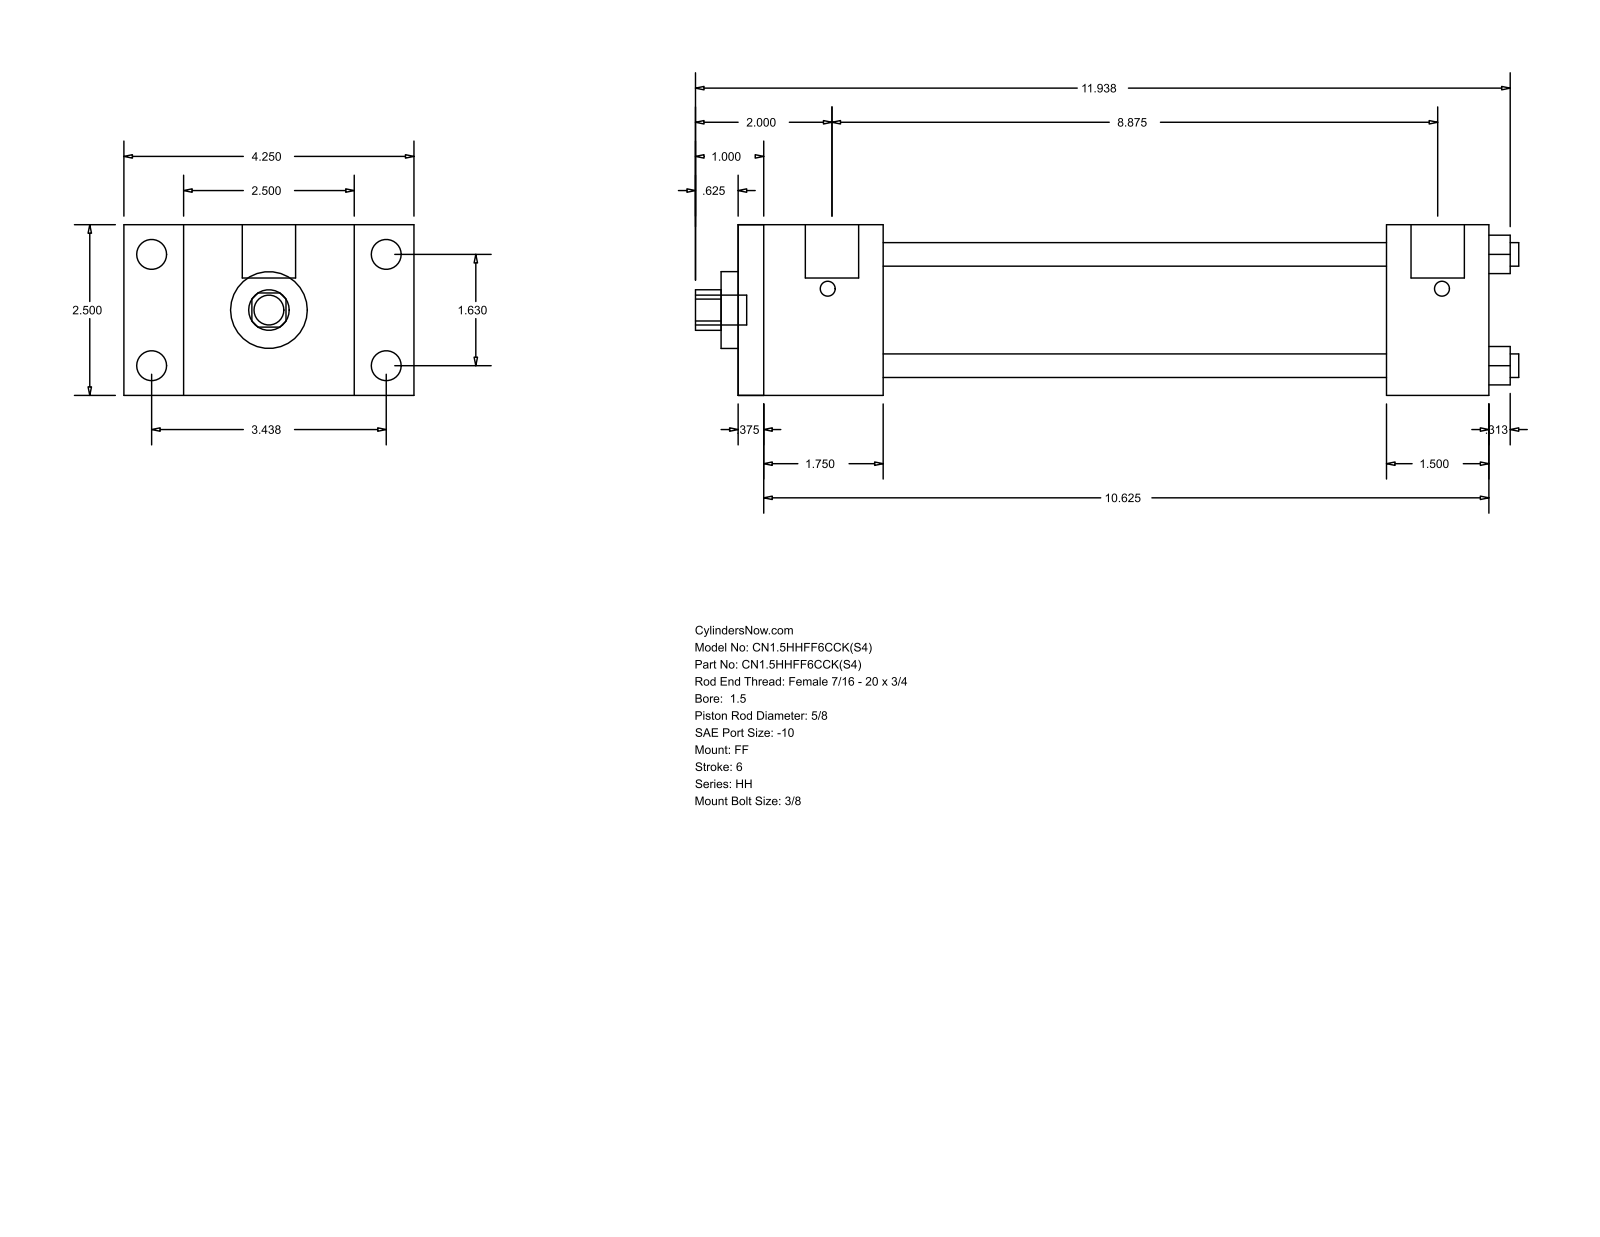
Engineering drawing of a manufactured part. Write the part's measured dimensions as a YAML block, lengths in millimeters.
part_name: "HH_FF__0150_0.625"
step_written_by: "GSSL Pune (CONFIG_CONTROL_DESIGN)"
units: millimeters
bodies: {solids: 0, faces: 92, planar: 64, cylindrical: 28, other: 0}
overall_size: [306.39, 107.95, 63.5]
round_holes:
  - {diameter: 8.76, count: 4}
  - {diameter: 15.88, count: 1}
  - {diameter: 28.57, count: 1}
  - {diameter: 44.45, count: 1}
round_bosses_or_shafts:
  - {diameter: 11.13, count: 4}
  - {diameter: 5.56, count: 4}
  - {diameter: 19.84, count: 2}
  - {diameter: 11.11, count: 1}
partial_cylinders:
  - {radius: 7.54, count: 1}
face_to_face_distances: [63.5, 279.39, 9.52, 269.87, 53.97, 44.45, 225.42, 241.3, 231.78, 187.33]
hole_center_spacings: [29.27, 41.4, 58.55]
